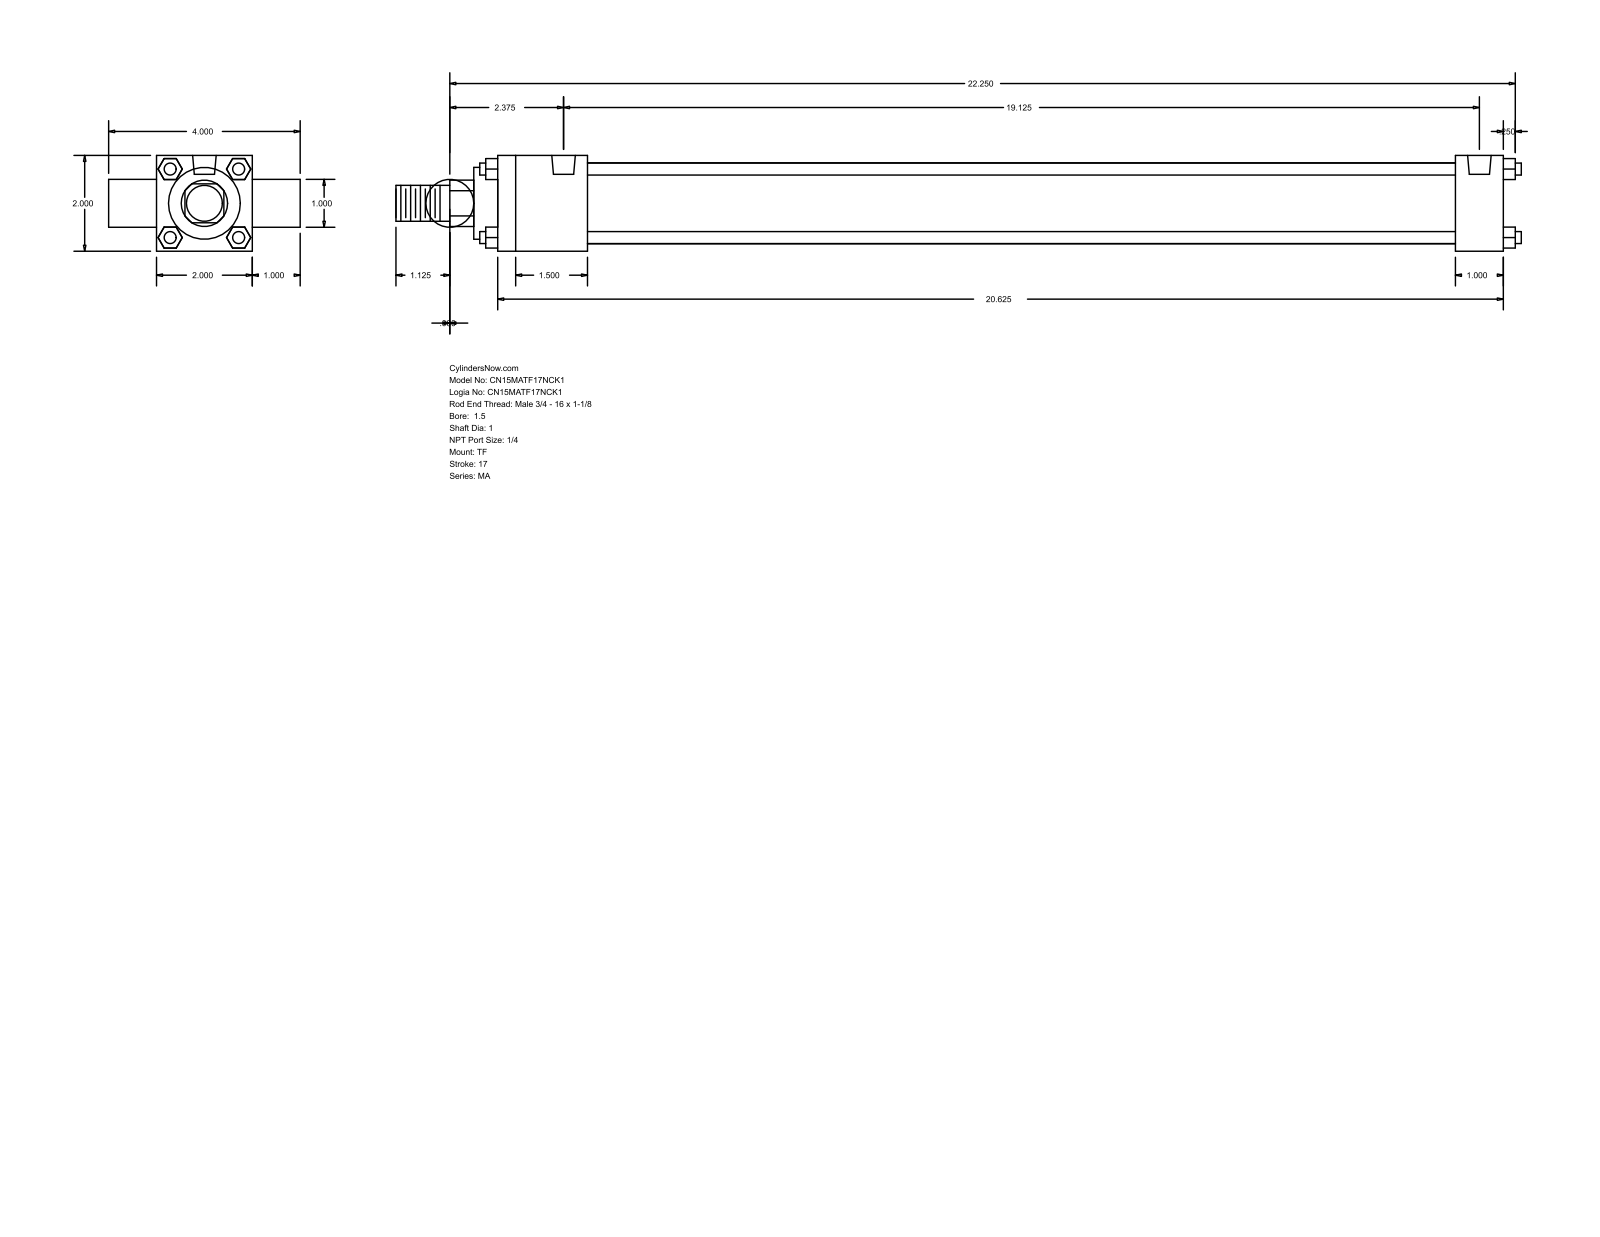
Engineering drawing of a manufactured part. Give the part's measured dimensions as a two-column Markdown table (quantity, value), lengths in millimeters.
| quantity | value |
| --- | --- |
| part name | MA_TF__0150_1 |
| STEP written by | GSSL Pune (CONFIG_CONTROL_DESIGN) |
| units | millimeters |
| bodies | 0 solids, 120 faces (92 planar, 28 cylindrical, 0 other) |
| overall size | 596.9 × 101.6 × 50.8 |
| round holes (diameter × count) | 7.94 × 3, 12.49 × 2 |
| round bosses / shafts (diameter × count) | 6.35 × 4, 25.4 × 2, 42.93 × 1, 38.1 × 1, 19.05 × 1 |
| partial cylindrical surfaces (radius × count) | 12.29 × 1 |
| main face-to-face distances | 50.8, 25.4, 533.4, 76.2, 6.35, 47.63, 508, 460.37, 485.77, 546.1 |
| hole center spacings | 485.77 |
